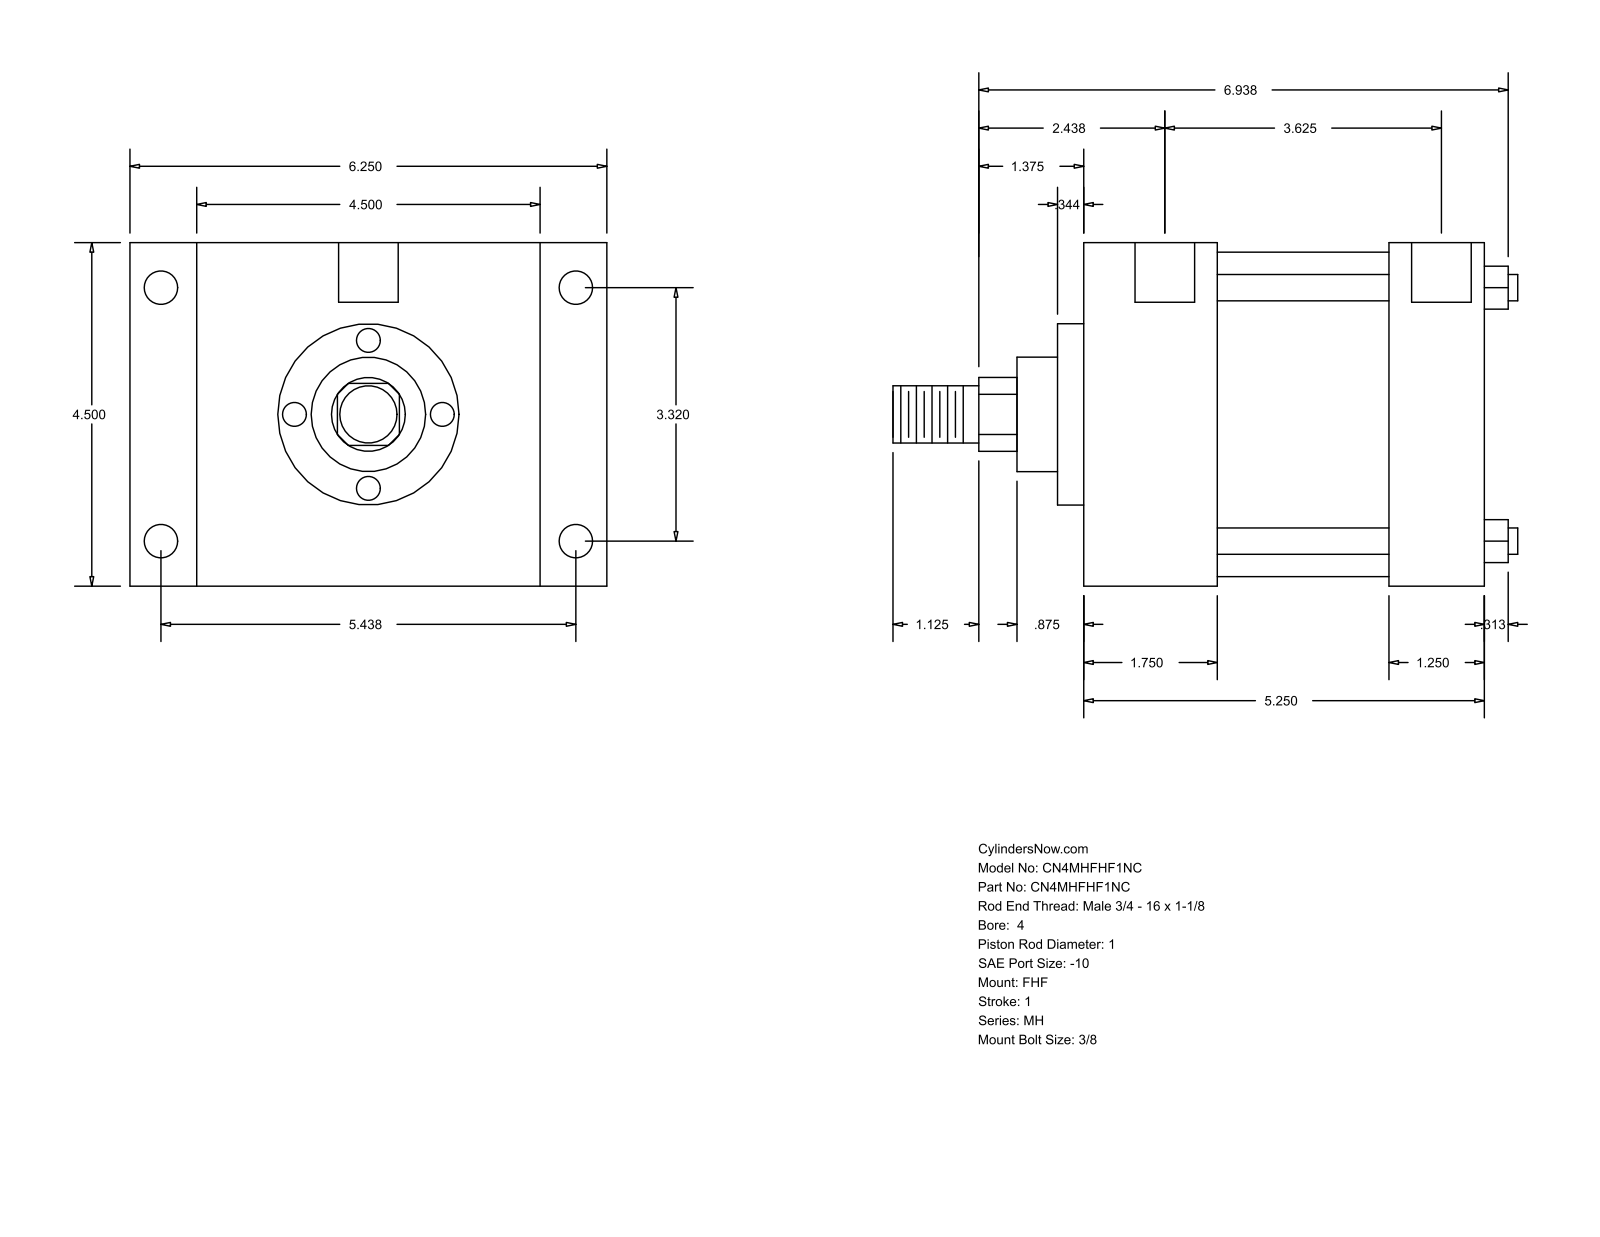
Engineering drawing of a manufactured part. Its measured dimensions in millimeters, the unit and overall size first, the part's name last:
Units: millimetres
Overall size (bounding box): 207.96 × 158.75 × 114.3
Round holes (diameter × count): ⌀8.73 ×4, ⌀11.13 ×4, ⌀19.84 ×2
Round bosses / shafts (diameter × count): ⌀8.76 ×4, ⌀107.95 ×1, ⌀60.33 ×1, ⌀38.1 ×1, ⌀25.4 ×1, ⌀19.05 ×1
Partial cylindrical surfaces — rounded edges, fillets, slot ends (radius × count): R12.29 ×1
Main face-to-face distances: 114.3, 133.36, 44.46, 88.9, 136.53, 22.23, 158.76, 101.61, 57.15, 31.75
Hole centre spacings: 1.58, 84.32, 93.66, 95.24, 138.12, 161.82, 92.08
Bodies: 0 solids, 90 faces (61 planar, 29 cylindrical, 0 other)
Part name (STEP PRODUCT): MH_FHF__0400_1
STEP written by: GSSL Pune (CONFIG_CONTROL_DESIGN)
